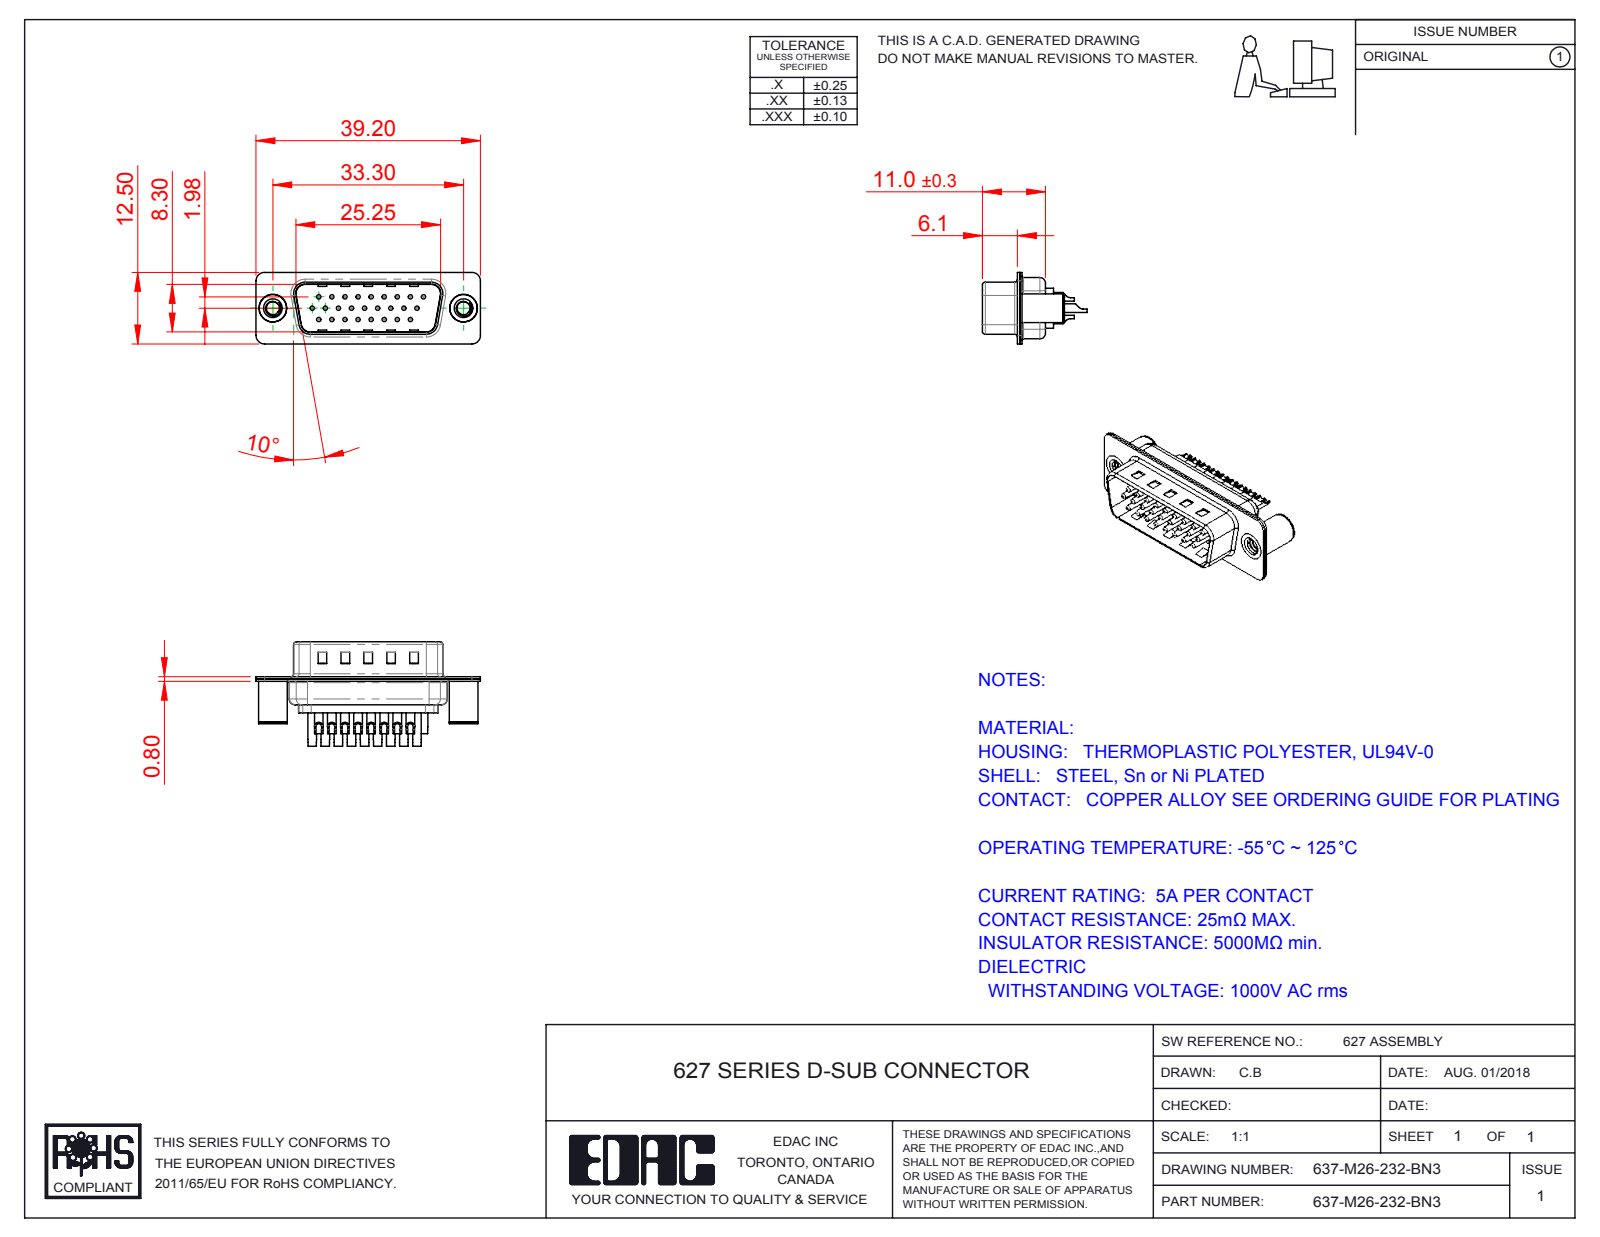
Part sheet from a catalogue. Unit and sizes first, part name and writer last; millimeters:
Units: millimetres
Overall size (bounding box): 39.2 × 18.25 × 12.5
Round holes (diameter × count): ⌀0.75 ×26, ⌀1 ×26, ⌀1.6 ×26, ⌀2 ×26, ⌀2.26 ×2, ⌀3.26 ×2, ⌀4 ×2, ⌀4.8 ×2
Round bosses / shafts (diameter × count): ⌀1.5 ×26, ⌀5 ×2, ⌀4.9 ×2
Partial cylindrical surfaces — rounded edges, fillets, slot ends (radius × count): R1.5 ×16, R2 ×12, R0.5 ×8, R1.6 ×8, R1 ×7, R0.25 ×4, R0.6 ×4, R0.65 ×4
Main face-to-face distances: 0.4, 0.8, 9.5, 9.1, 8.7, 9.9, 0.75, 0.35, 1.2, 1.9
Hole centre spacings: 3.96, 2.28, 4.57, 6.05, 2.29, 8.24, 6.86, 10.48
Volume: 2 118 mm³ · Surface area: 6 331 mm²
Bodies: 31 solids, 1336 faces (373 planar, 573 cylindrical, 390 other)
Part name (STEP PRODUCT): 637M Housing_26 Contacts; 637M Shell Front_26 Contacts; 637M Contact Row 2_32; 637M Shell Rear_26 Contacts (+4 more)
STEP written by: SolidWorks 2016 (CONFIG_CONTROL_DESIGN)
